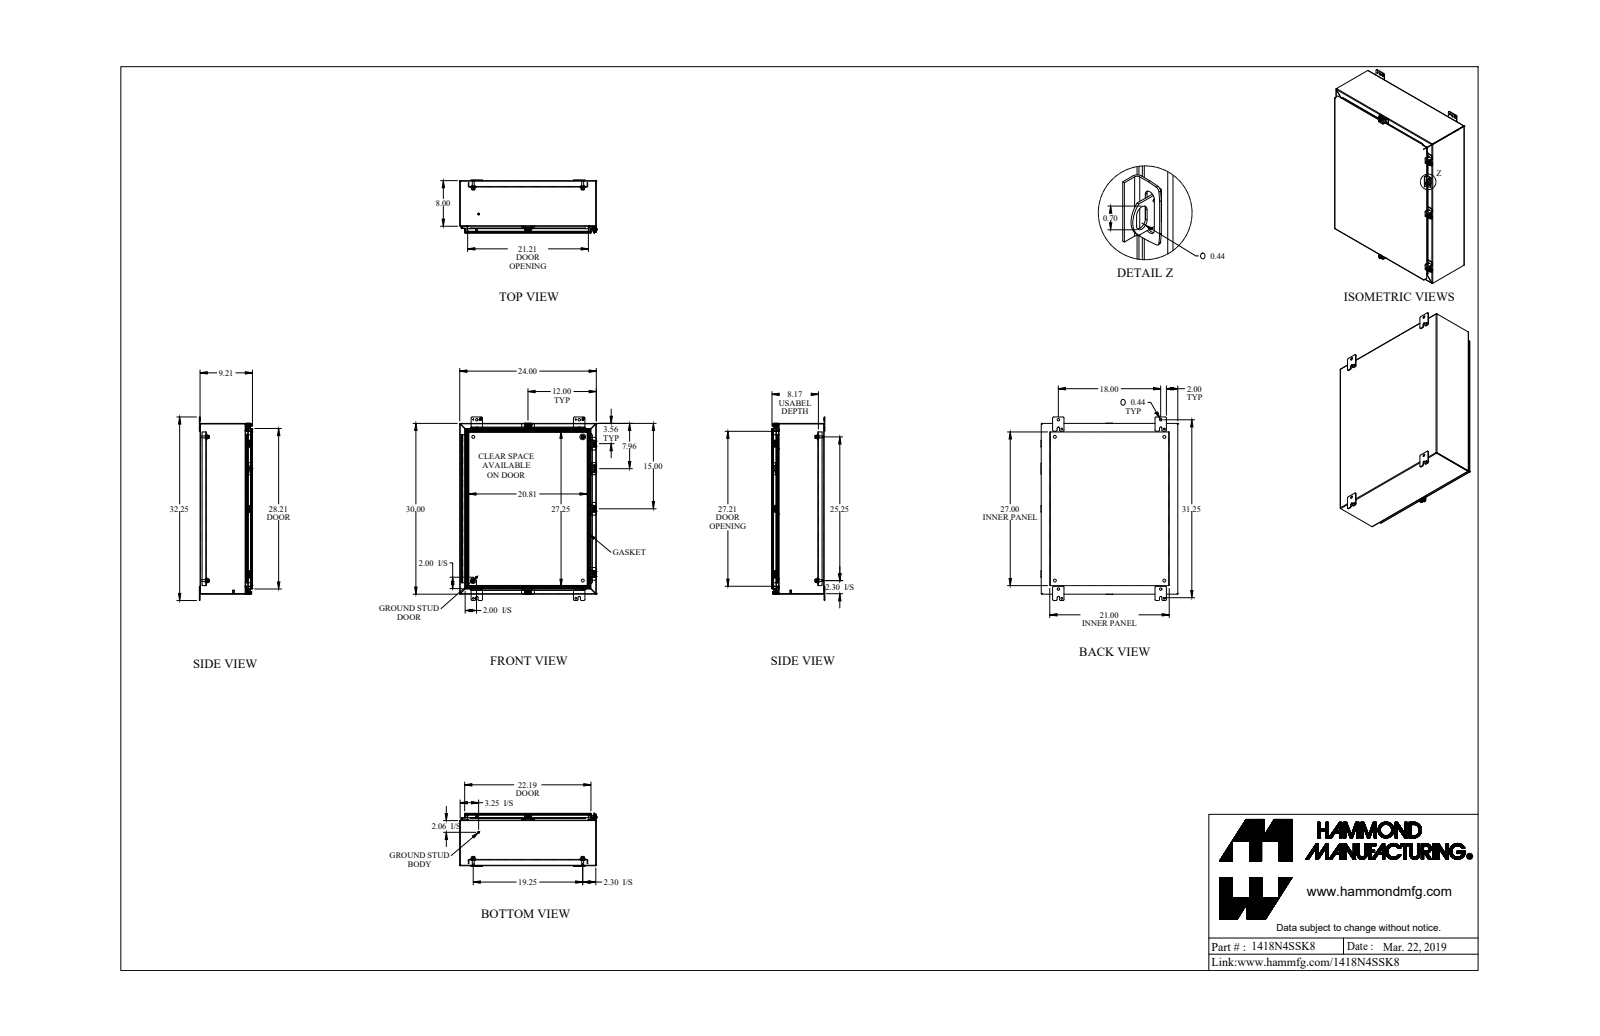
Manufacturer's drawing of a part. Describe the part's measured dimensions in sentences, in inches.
The part is named "1418N4SSK8_Default". Its 3-D file was written by "SolidWorks 2019 (CONFIG_CONTROL_DESIGN)". It is 43 solids with 1687 faces: 1037 planar, 556 cylindrical and 94 other. Overall it measures 32.25 by 24.063 by 9.375 inches. Its volume is 258.2 cubic inches and its surface area 6 773 square inches. Round holes: 5 of diameter 0.213, 5 of diameter 0.265, 5 of diameter 0.375, 4 of diameter 0.313, 4 of diameter 0.437, 4 of diameter 0.5, 2 of diameter 0.307, 2 of diameter 0.445, 1 of diameter 0.125, 1 of diameter 0.187. Round bosses or shafts: 5 of diameter 0.5, 5 of diameter 0.39, 5 of diameter 0.244, 4 of diameter 0.65, 4 of diameter 0.375, 4 of diameter 0.332, 2 of diameter 1, 2 of diameter 0.313. Partial cylindrical surfaces (rounded edges, fillets, slot ends): 27 of radius 0.048, 27 of radius 0.143, 26 of radius 0.188, 24 of radius 0.036, 24 of radius 0.108, 24 of radius 0.25, 10 of radius 0.125, 10 of radius 0.141. The main face-to-face distances are 0.072, 0.072, 9.066, 9.138, 9.138, 9.21, 0.095, 0.937, 1.009, 8.106. The hole center spacings are 1.736, 3.065, 9.857, 18, 25.25, 29.018, 29.75, 31.751.
